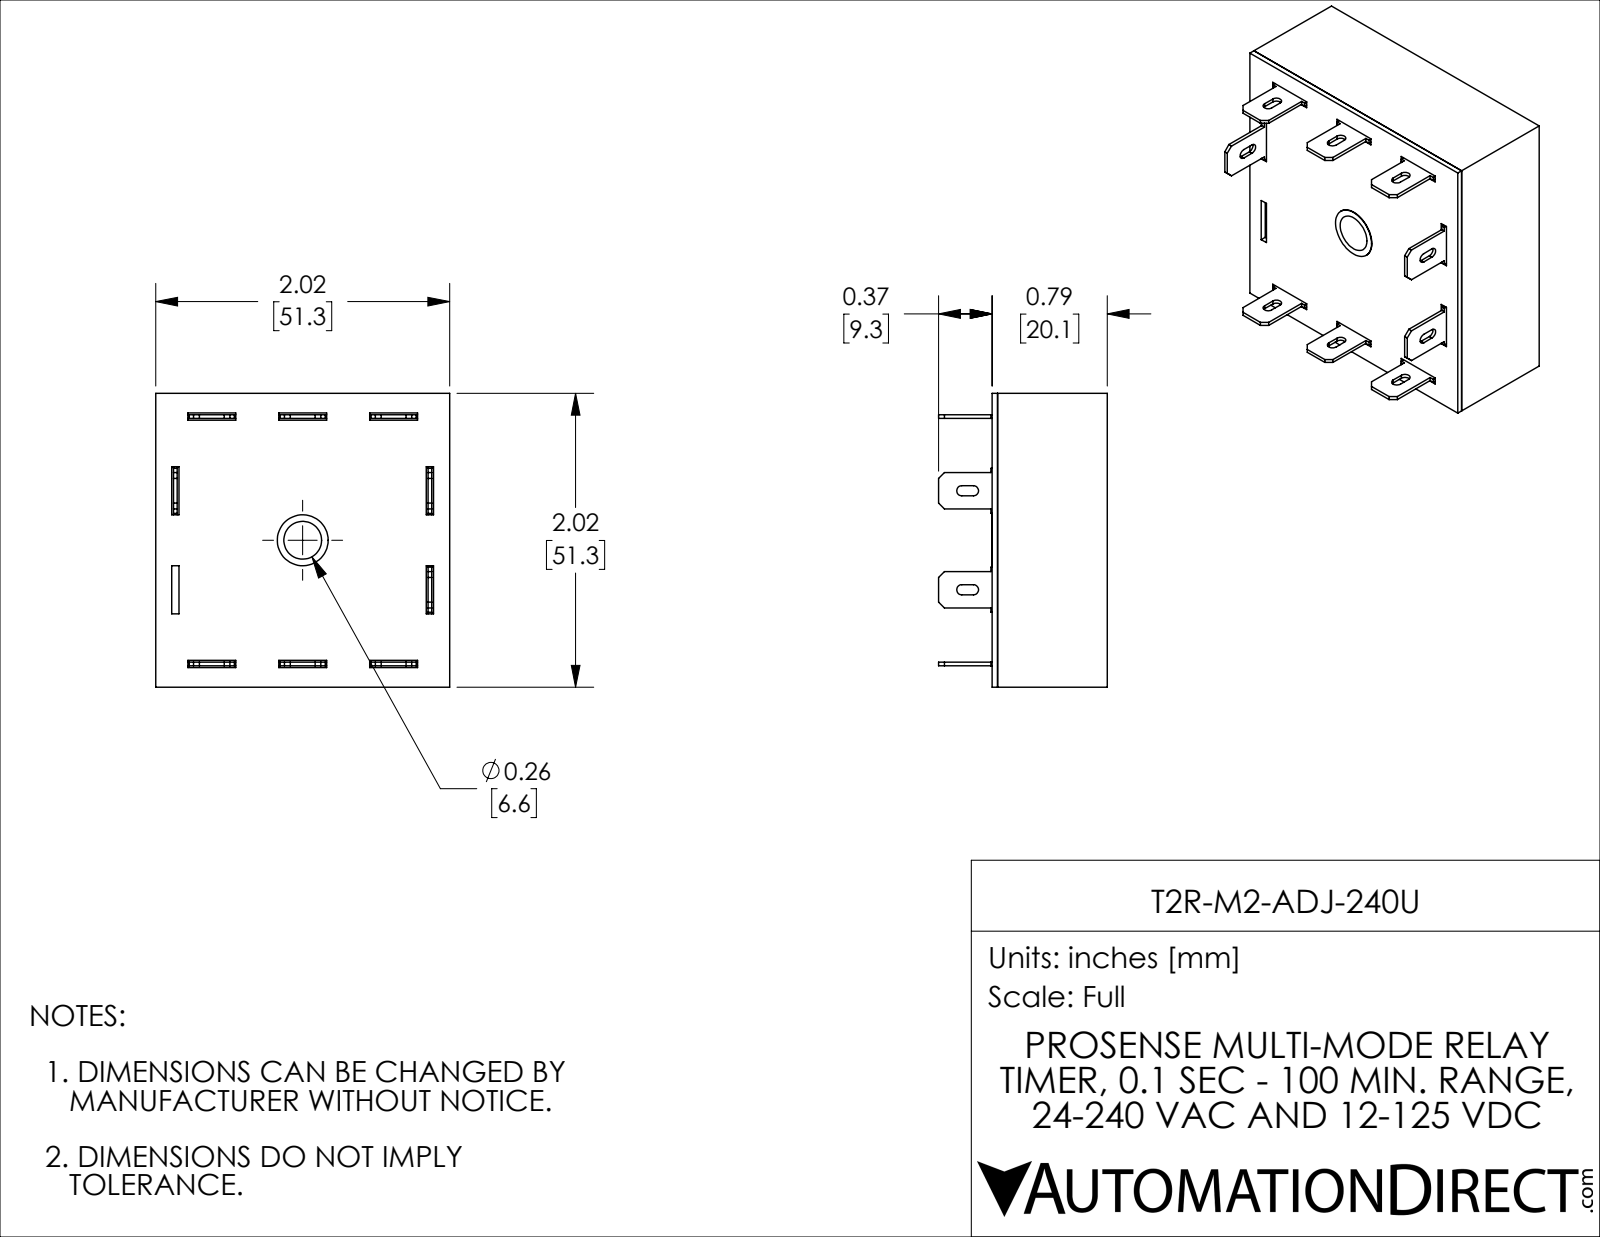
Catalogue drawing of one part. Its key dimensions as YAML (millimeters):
part_name: "T2R-M2-ADJ-240U"
step_written_by: "SolidWorks 2021 (CONFIG_CONTROL_DESIGN)"
units: millimeters
bodies: {solids: 11, faces: 280, planar: 256, cylindrical: 22, other: 2}
overall_size: [51.31, 51.31, 29.46]
volume: 11178
surface_area: 23301
round_holes:
  - {diameter: 8.89, count: 1}
partial_cylinders:
  - {radius: 0.89, count: 10}
face_to_face_distances: [1.14, 50.16, 19.15, 20.12, 0.97, 18.01, 18.98, 51.3, 3.74, 47.56]
